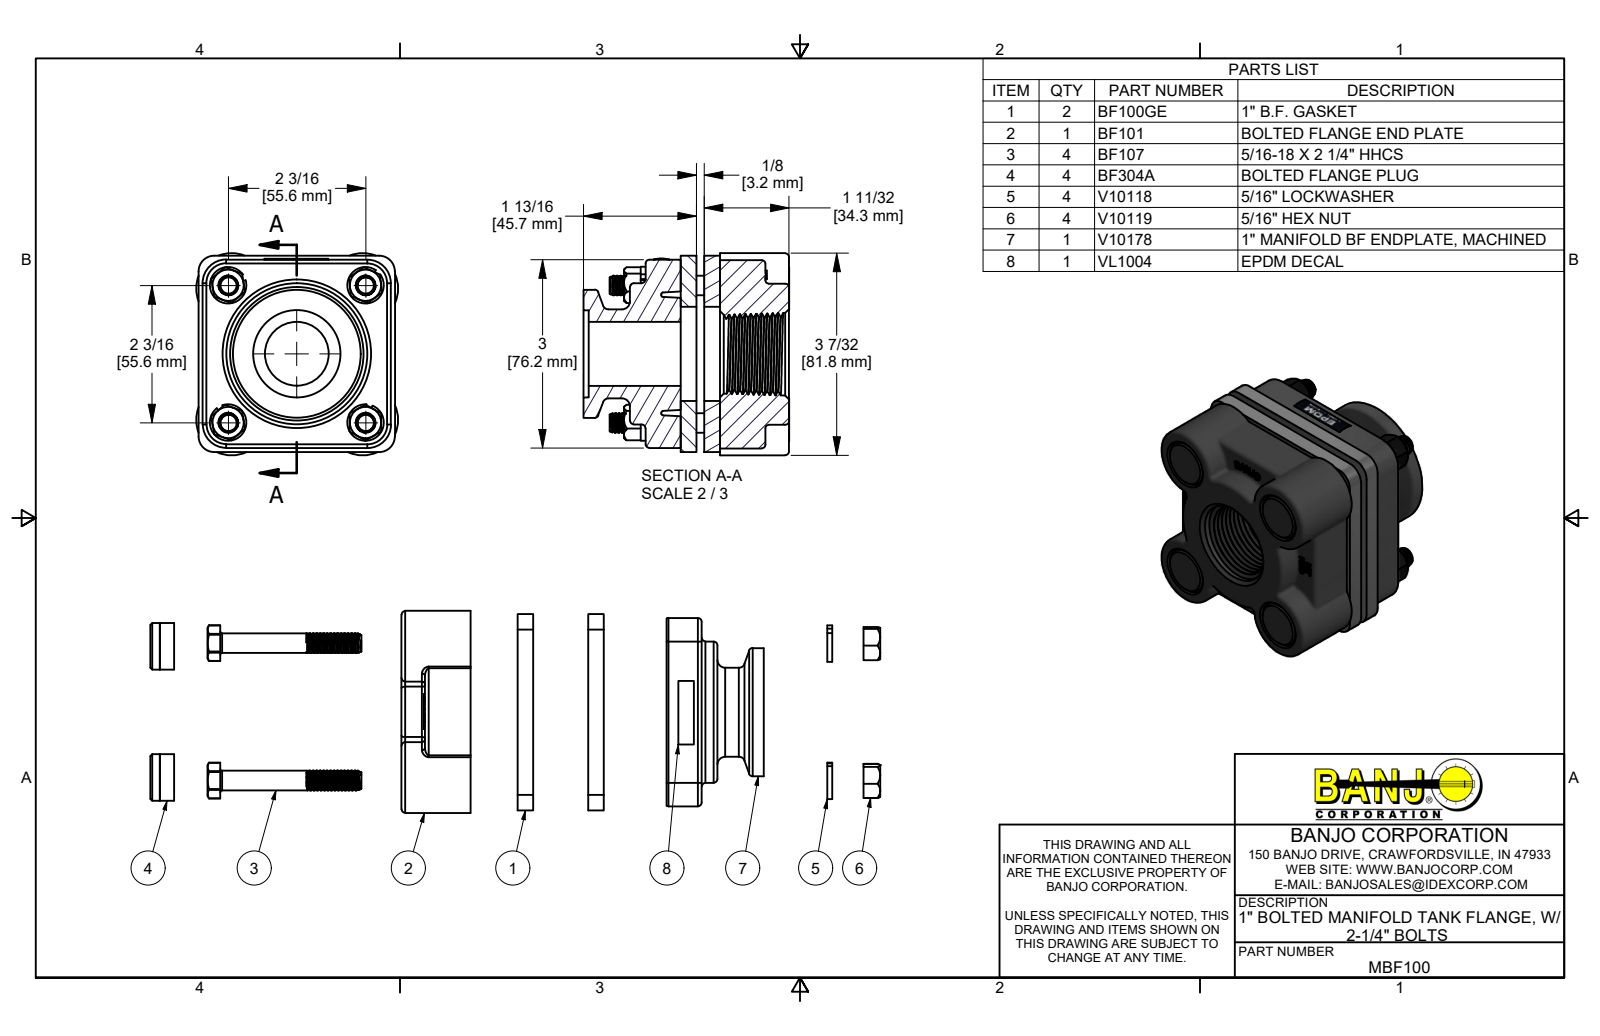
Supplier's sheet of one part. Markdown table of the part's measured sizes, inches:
| quantity | value |
| --- | --- |
| part name | MBF100; BF101; BF106; BF304AT (+7 more) |
| STEP written by | Autodesk Inventor 2017 (AUTOMOTIVE_DESIGN) |
| units | inches |
| bodies | 21 solids, 1007 faces (447 planar, 220 cylindrical, 340 other) |
| overall size | 3.275 × 3.22 × 3.22 |
| volume | 18.71 in³ |
| surface area | 152.4 in² |
| round holes (diameter × count) | 0.252 × 4, 0.313 × 4, 0.322 × 4, 0.34 × 4, 0.344 × 4, 0.35 × 4, 0.72 × 4, 0.745 × 4, 1.02 × 1, 1.39 × 1, 1.5 × 1 |
| round bosses / shafts (diameter × count) | 0.742 × 4, 0.583 × 4, 0.48 × 4, 0.313 × 4, 0.305 × 4, 0.245 × 4, 2.25 × 1, 2.04 × 1 |
| partial cylindrical surfaces (radius × count) | 0.03 × 24, 0.06 × 20, 0.05 × 8, 0.063 × 4, 0.25 × 4, 0.375 × 4, 0.565 × 4, 0.375 × 1 |
| main face-to-face distances | 0.25, 0.375, 0.625, 0.125, 0.81, 1.185, 1.475, 1.1, 1.725, 1.35 |
| hole center spacings | 2.188, 2.194, 2.139, 1.547, 2.2, 3.025, 3.094, 3.103 |
